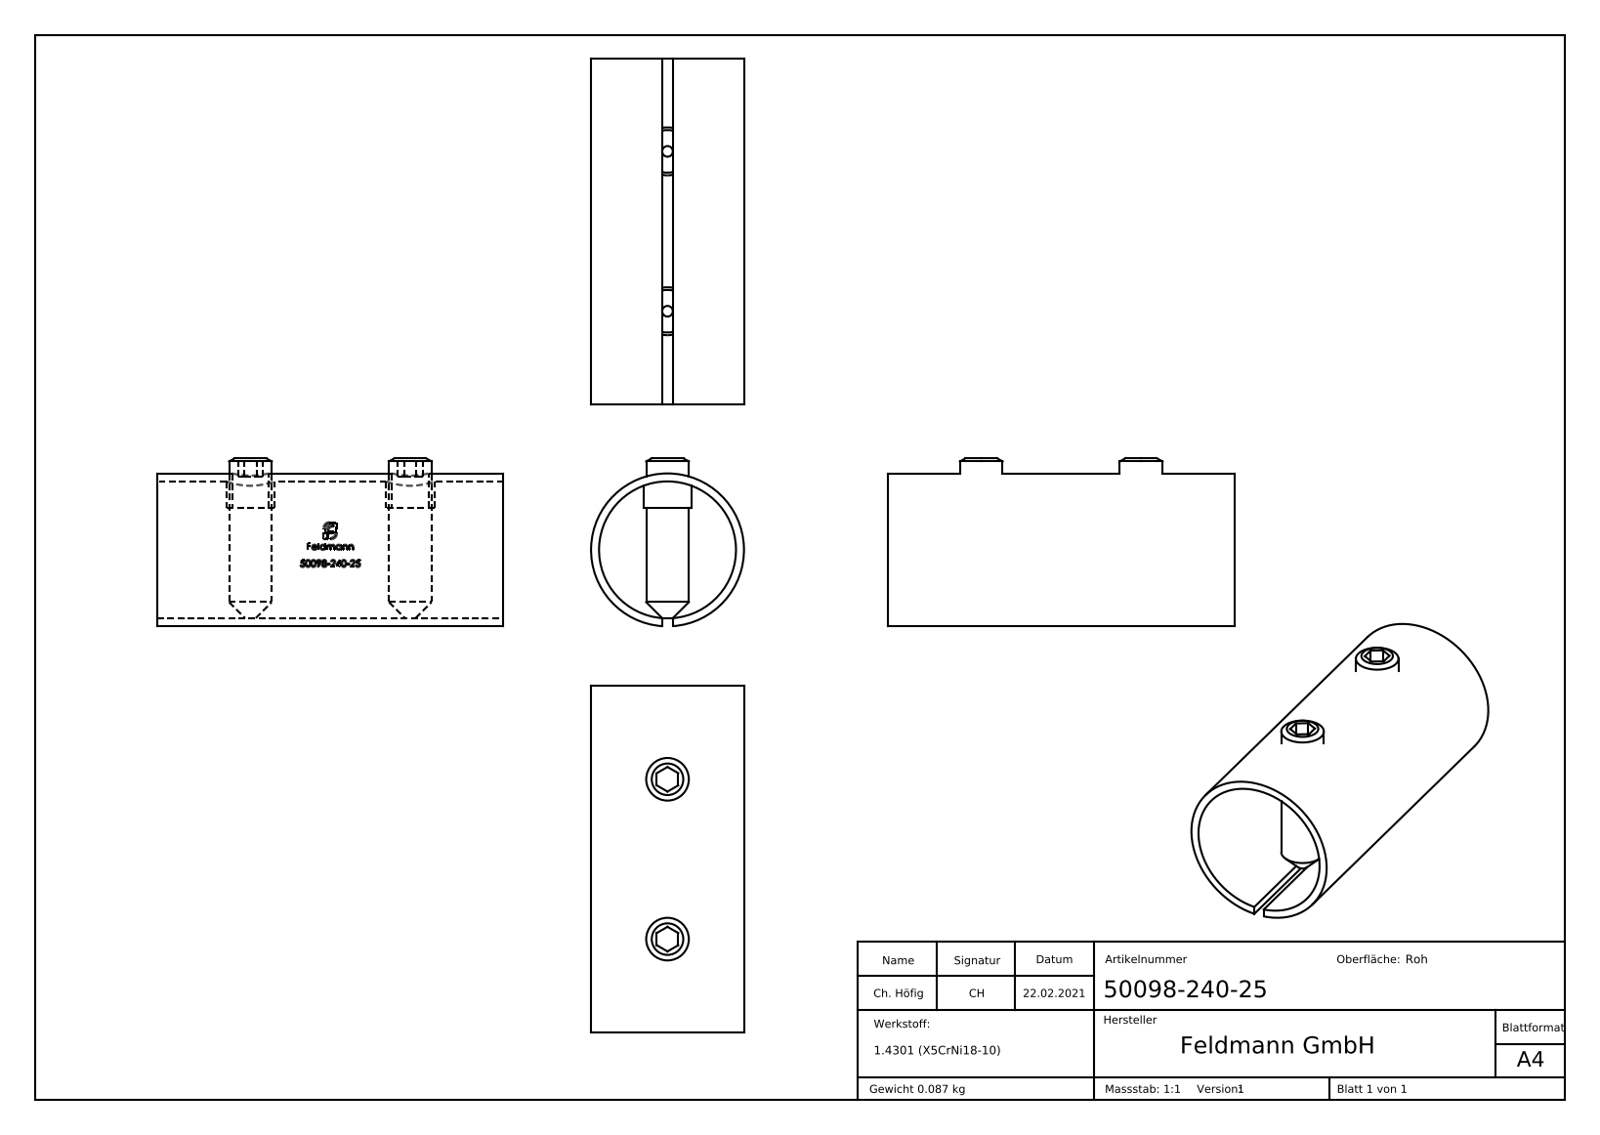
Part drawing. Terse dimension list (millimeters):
name: 50098-240-25 Teil1; 50098-240-25; 50098-240-25 DIN 914 M8 x 30; 50098-240-25 Teil1_50098-240-25 Teil1 Keyshot (+1 more)
written by: SolidWorks 2018 (CONFIG_CONTROL_DESIGN)
unit: mm
bodies: 3 solids, 58 faces (24 planar, 8 cylindrical, 26 other)
size: 65 × 31.5 × 28.7
volume: 10 417 mm³; area: 14 174 mm²
holes: 2× ⌀6.8, 1× ⌀25.7
bosses: 2× ⌀9, 2× ⌀8, 1× ⌀28.7
face distances: 65, 2, 4, 25.98, 1, 3, 5.84, 29.98, 21.98, 9.34
hole spacings: 30
